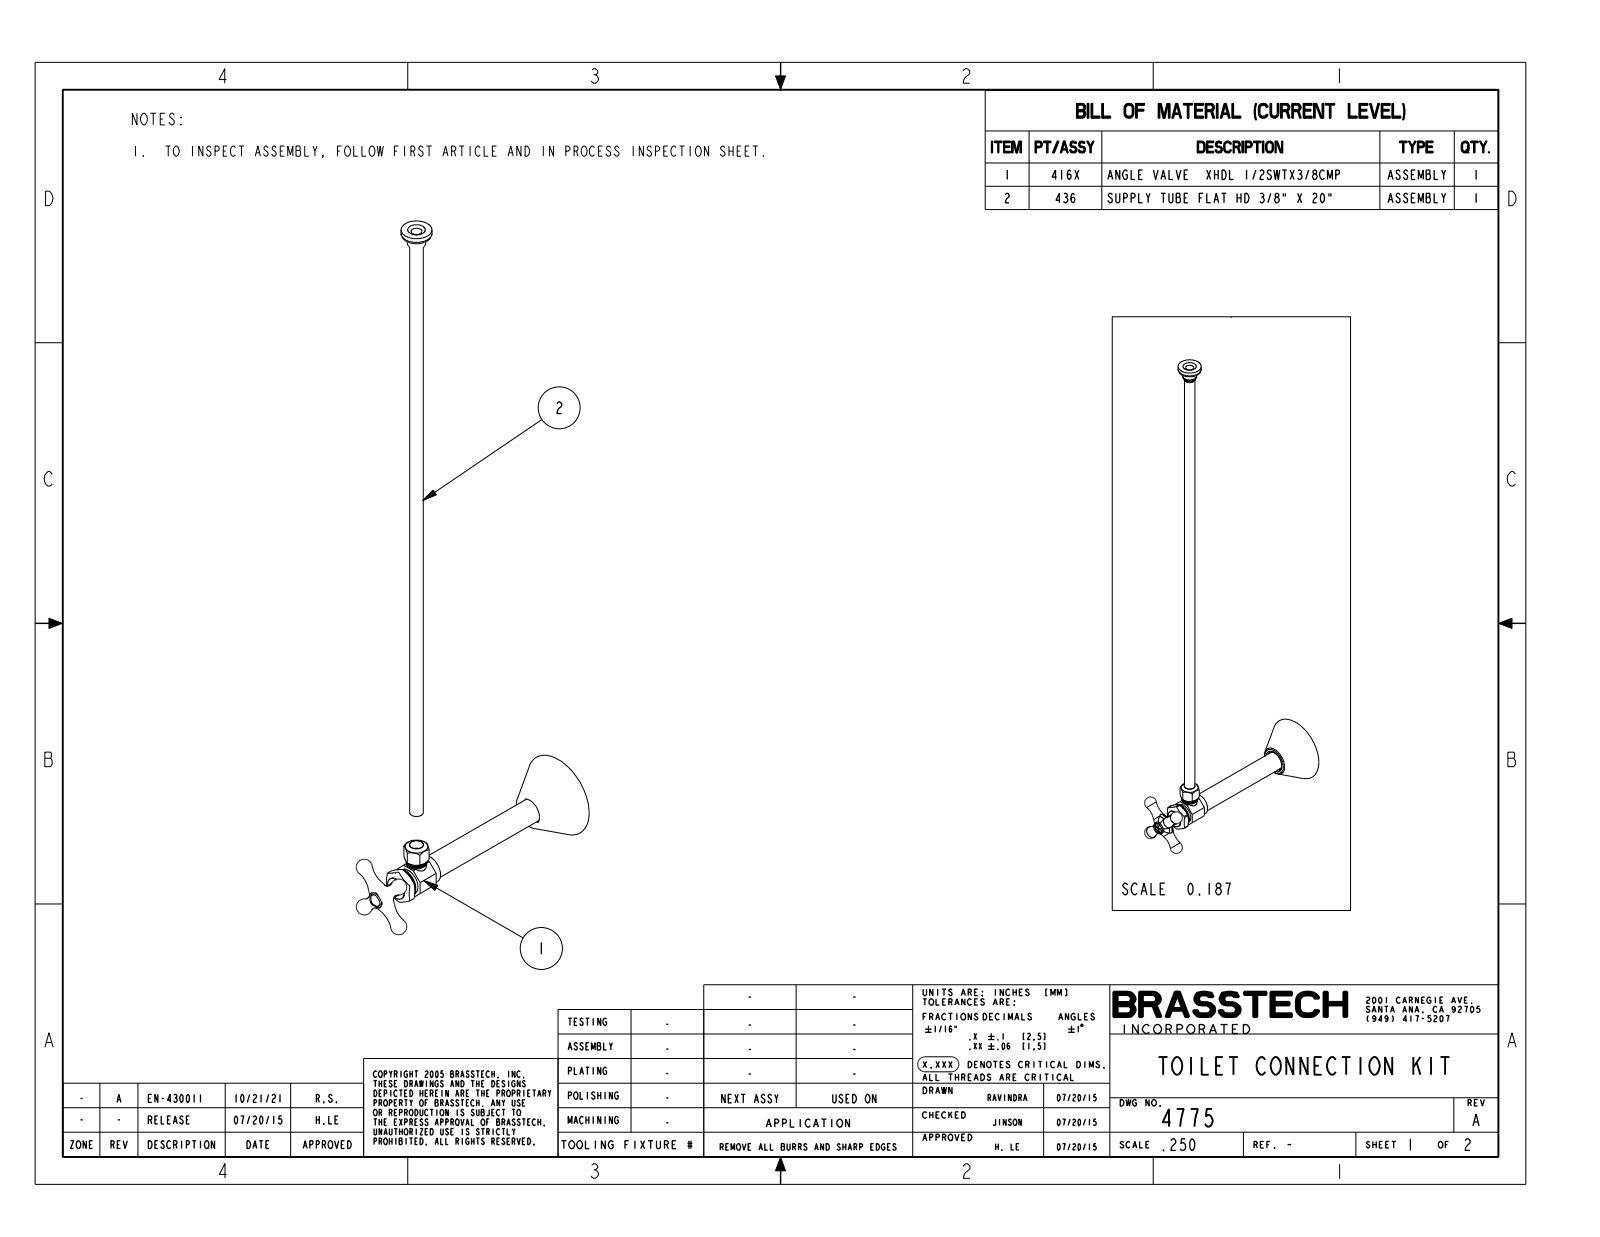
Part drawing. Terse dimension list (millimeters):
name: 50673; 50359; 50677; 50674 (+8 more)
written by: CREO PARAMETRIC BY PTC INC, 2018400 (AUTOMOTIVE_DESIGN)
unit: mm
bodies: 13 solids, 705 faces (220 planar, 255 cylindrical, 230 other)
size: 537.8 × 181.5 × 61
volume: 36 310 mm³; area: 70 390 mm²
holes: 2× ⌀15.7, 1× ⌀3.3, 1× ⌀4.4, 1× ⌀4.9, 1× ⌀7.6, 1× ⌀8.4, 1× ⌀8.5, 1× ⌀9.6, 1× ⌀9.7, 1× ⌀9.7, 1× ⌀9.9, 1× ⌀9.9
bosses: 2× ⌀20.3, 1× ⌀21.8, 1× ⌀21.5, 1× ⌀20.7, 1× ⌀19.1, 1× ⌀18.7, 1× ⌀17.3, 1× ⌀16
rounds: 18× R0.3, 6× R1.3, 1× R4.3, 1× R4.7, 1× R4.7
face distances: 22.9, 3.2, 0.8, 22.5, 15.9, 10.1, 10.9, 1.5, 4.7, 2.9
hole spacings: 32.8
